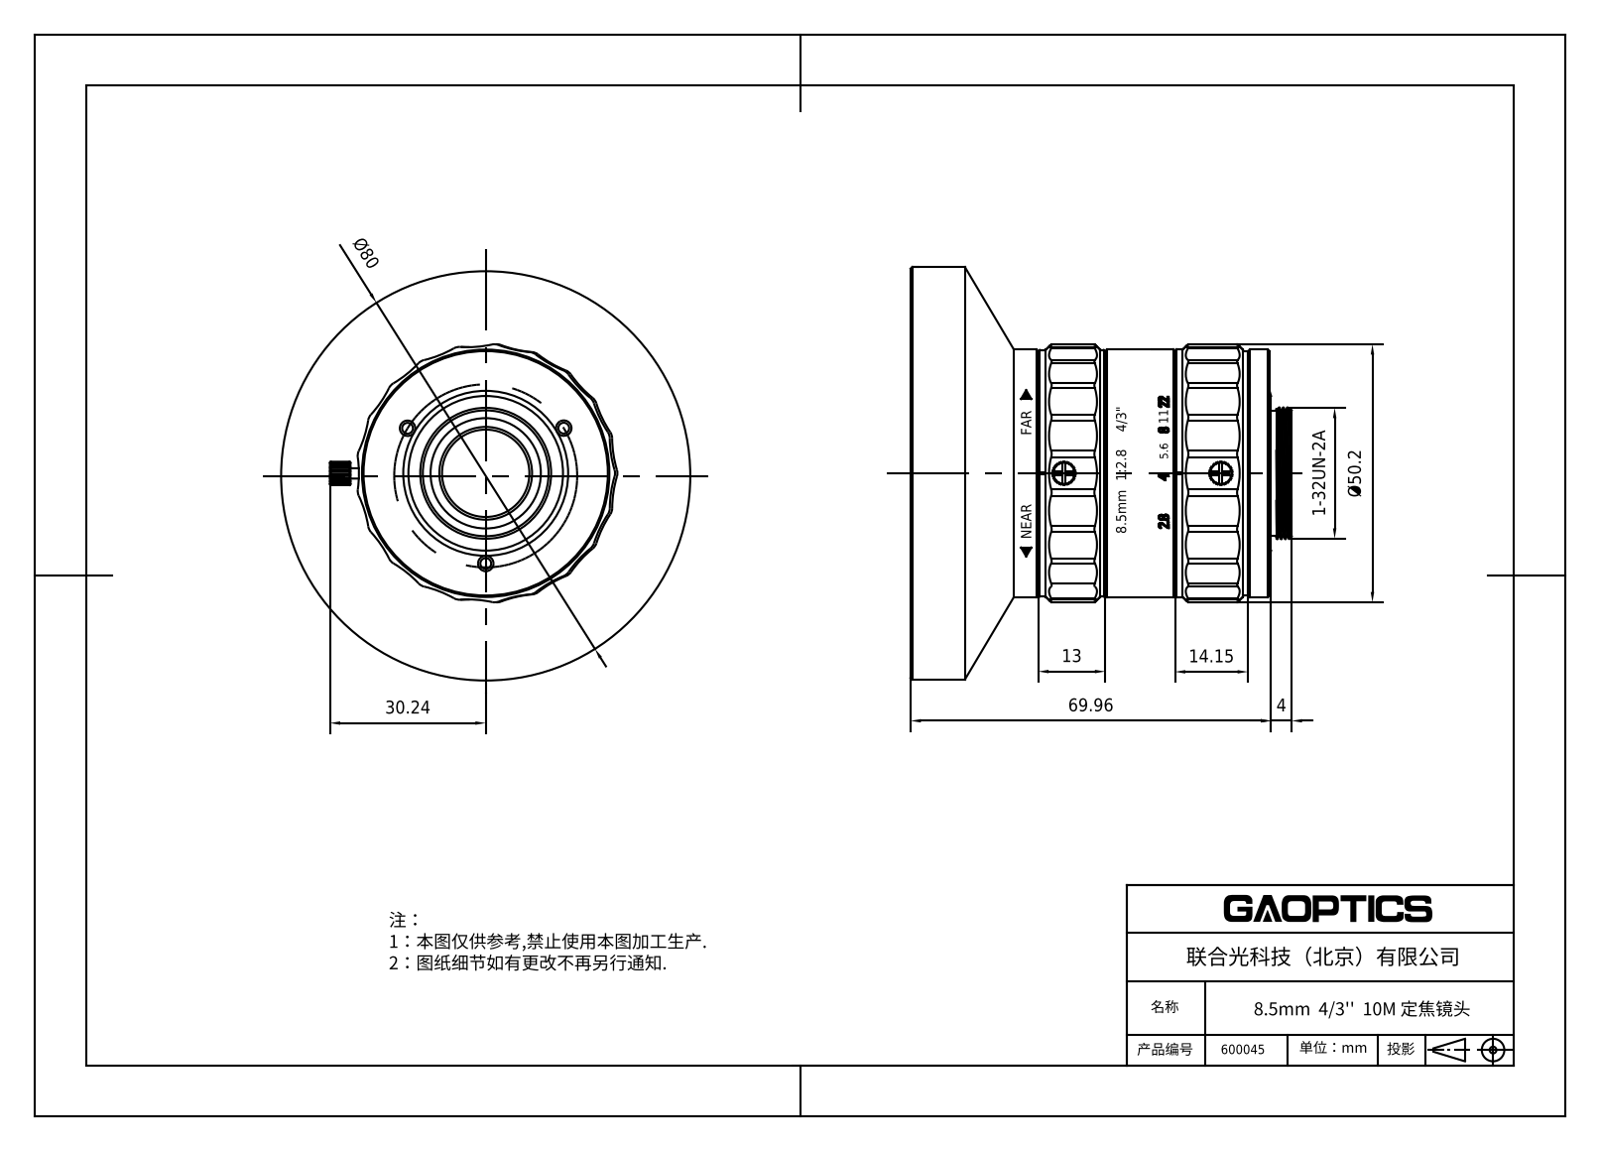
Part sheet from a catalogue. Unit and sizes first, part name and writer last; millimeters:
Units: millimetres
Overall size (bounding box): 81.38 × 80.57 × 80
Round holes (diameter × count): ⌀1.6 ×7, ⌀1.3 ×3, ⌀1.9 ×3, ⌀2.1 ×3, ⌀3 ×3, ⌀1.8 ×1, ⌀21.4 ×1, ⌀23.6 ×1, ⌀24.07 ×1, ⌀24.2 ×1, ⌀25 ×1, ⌀26.06 ×1
Round bosses / shafts (diameter × count): ⌀47.8 ×3, ⌀48 ×2, ⌀46 ×2, ⌀2 ×2, ⌀80 ×1, ⌀54.8 ×1, ⌀47.4 ×1, ⌀43.8 ×1
Partial cylindrical surfaces — rounded edges, fillets, slot ends (radius × count): R2.15 ×42, R22 ×42, R1.5 ×4, R1.4 ×3, R2.25 ×2, R24.5 ×2, R0.76 ×1, R19.5 ×1
Main face-to-face distances: 0.5, 1, 1.5, 2, 1.03, 0.34, 1.37, 2.5, 55.39, 55.73
Hole centre spacings: 17.5, 26.89, 4.05, 8.93, 23.3, 24.74, 30.31, 30.32
Volume: 131 428 mm³ · Surface area: 36 345 mm²
Bodies: 2 solids, 1653 faces (964 planar, 403 cylindrical, 286 other)
Part name (STEP PRODUCT): 600045
STEP written by: SolidWorks 2020 (CONFIG_CONTROL_DESIGN)
